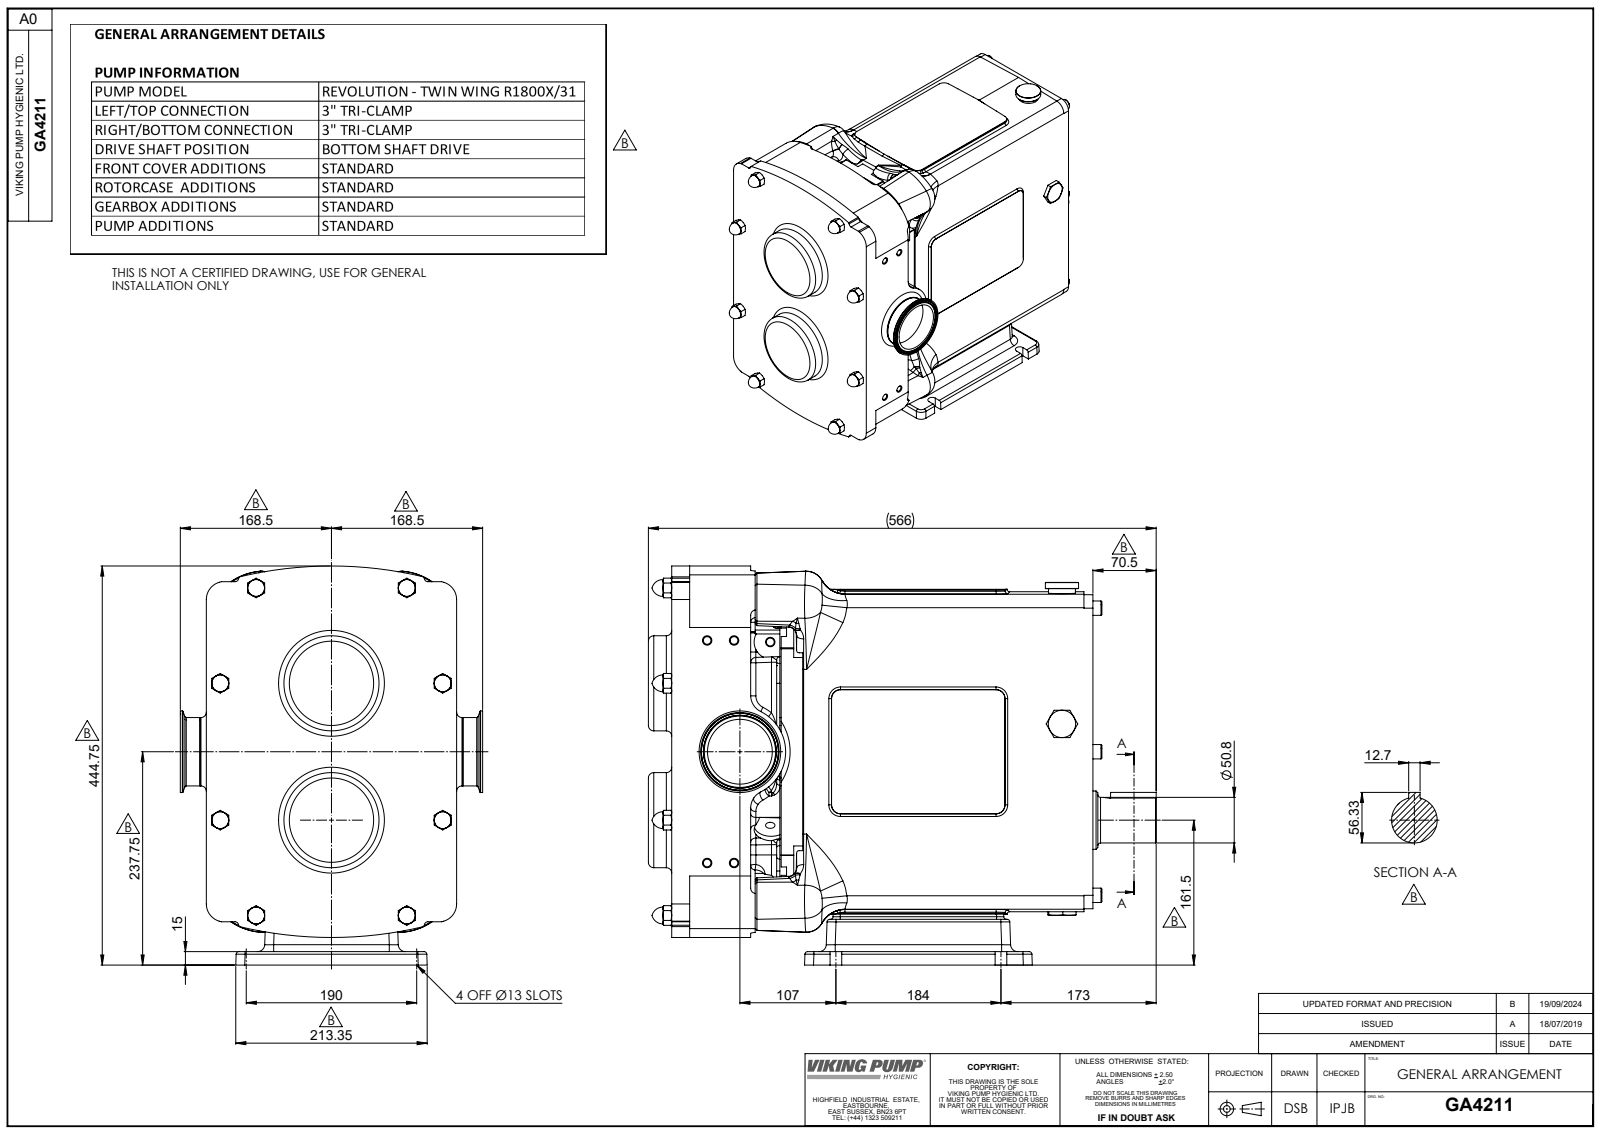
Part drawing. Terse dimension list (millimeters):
name: Copy of R1800 CPP H BSD^GA4211; Copy of RA94-5121-55M^GA4211; GA4211
written by: SolidWorks 2023 (AUTOMOTIVE_DESIGN)
unit: mm
bodies: 13 solids, 1544 faces (495 planar, 355 cylindrical, 694 other)
size: 566 × 444.75 × 337
volume: 37 360 000 mm³; area: 1 190 000 mm²
holes: 4× ⌀8.5, 3× ⌀8.8, 1× ⌀10.2, 1× ⌀10.5, 1× ⌀35, 1× ⌀72.25, 1× ⌀149
bosses: 6× ⌀16, 2× ⌀106, 1× ⌀94, 1× ⌀91, 1× ⌀76.2, 1× ⌀65, 1× ⌀50.8, 1× ⌀37
rounds: 44× R3, 36× R6, 30× R10, 16× R5, 14× R4, 10× R8, 8× R15, 6× R0.74
face distances: 190, 469.5, 3, 193, 41.5, 44.5, 234.5, 237.5, 323.5, 146
hole spacings: 30, 40.39, 70.37, 124.17, 126.85, 129.26, 248, 249.53
